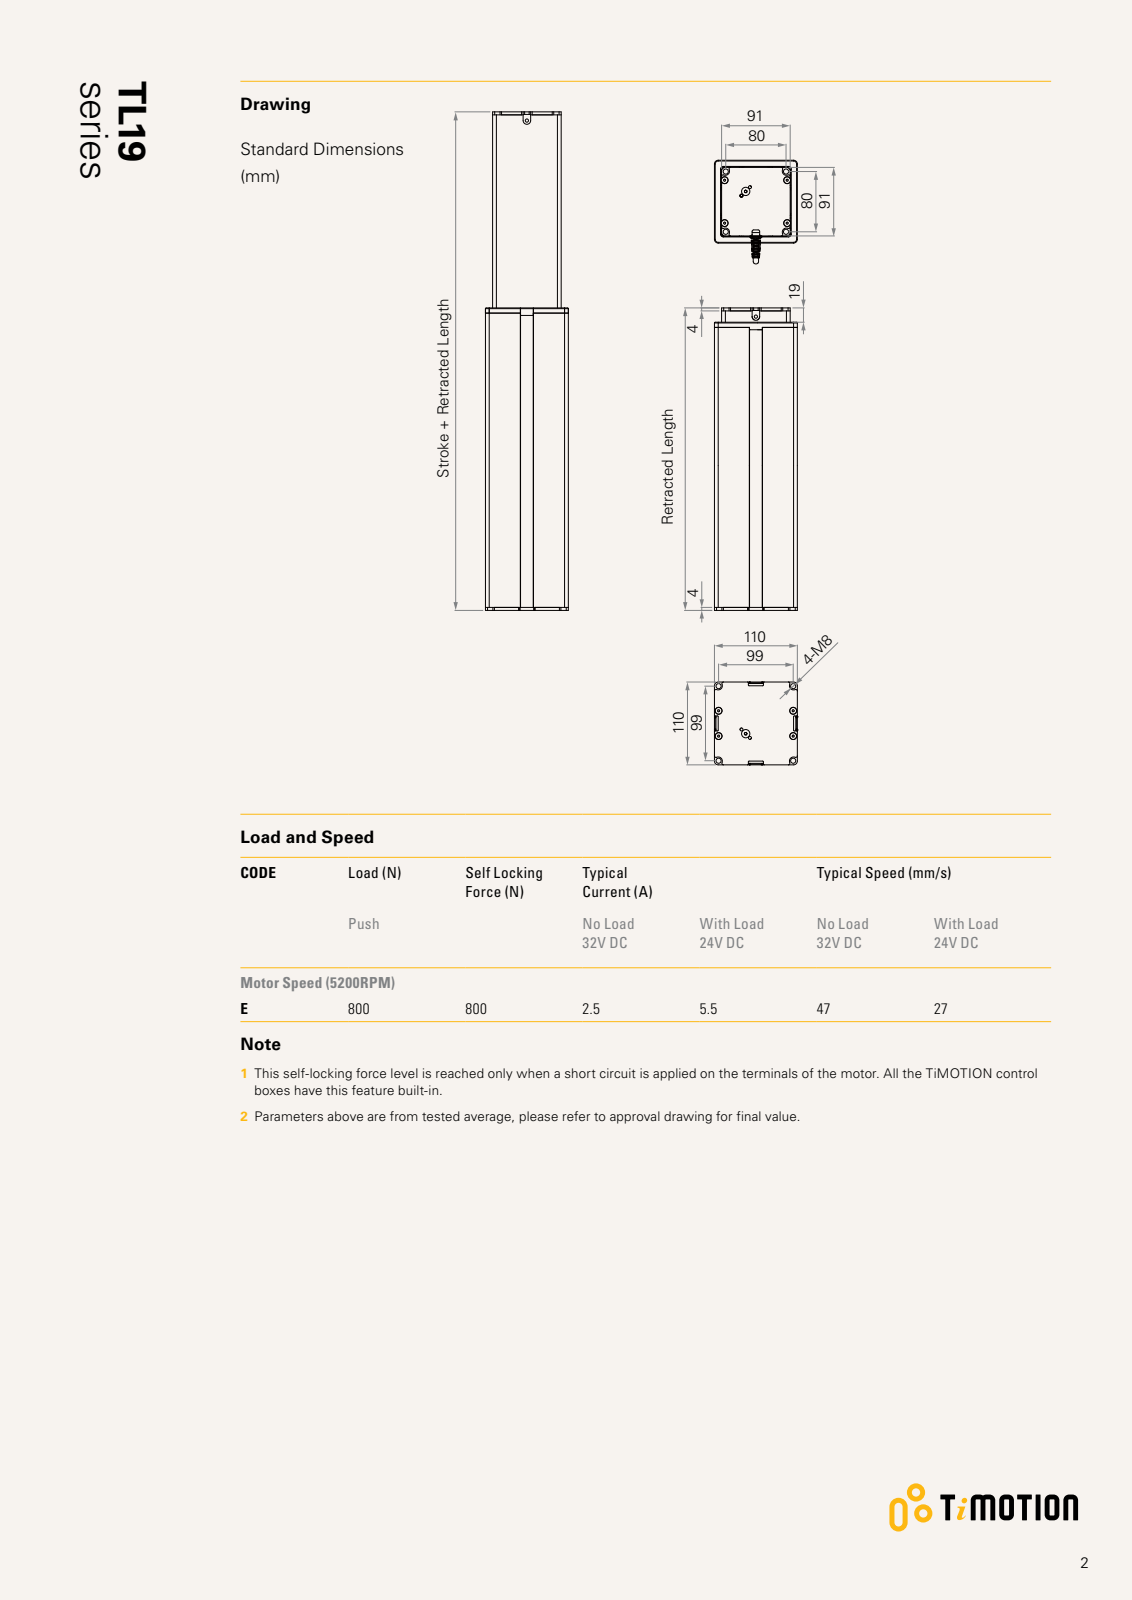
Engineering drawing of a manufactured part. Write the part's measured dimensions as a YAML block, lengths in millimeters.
part_name: "TL19"
step_written_by: "SolidWorks 2015 (CONFIG_CONTROL_DESIGN)"
units: millimeters
bodies: {solids: 15, faces: 1823, planar: 532, cylindrical: 1203, other: 88}
overall_size: [625, 110, 110]
volume: 2350000
surface_area: 1180000
round_holes:
  - {diameter: 4.2, count: 8}
  - {diameter: 6.8, count: 8}
  - {diameter: 9.2, count: 8}
  - {diameter: 4, count: 4}
  - {diameter: 6.2, count: 2}
  - {diameter: 11, count: 2}
round_bosses_or_shafts:
  - {diameter: 4, count: 8}
  - {diameter: 3.6, count: 8}
  - {diameter: 6, count: 2}
partial_cylinders:
  - {radius: 0.2, count: 238}
  - {radius: 1, count: 58}
  - {radius: 0.3, count: 44}
  - {radius: 2, count: 44}
  - {radius: 0.5, count: 36}
  - {radius: 3, count: 20}
  - {radius: 1.6, count: 16}
  - {radius: 1.9, count: 16}
face_to_face_distances: [100.5, 9.5, 4, 14, 86.5, 4.5, 96, 3.5, 98.5, 2]
hole_center_spacings: [90, 99, 8, 11.6, 13.44, 14.17, 22.47, 25.07]
